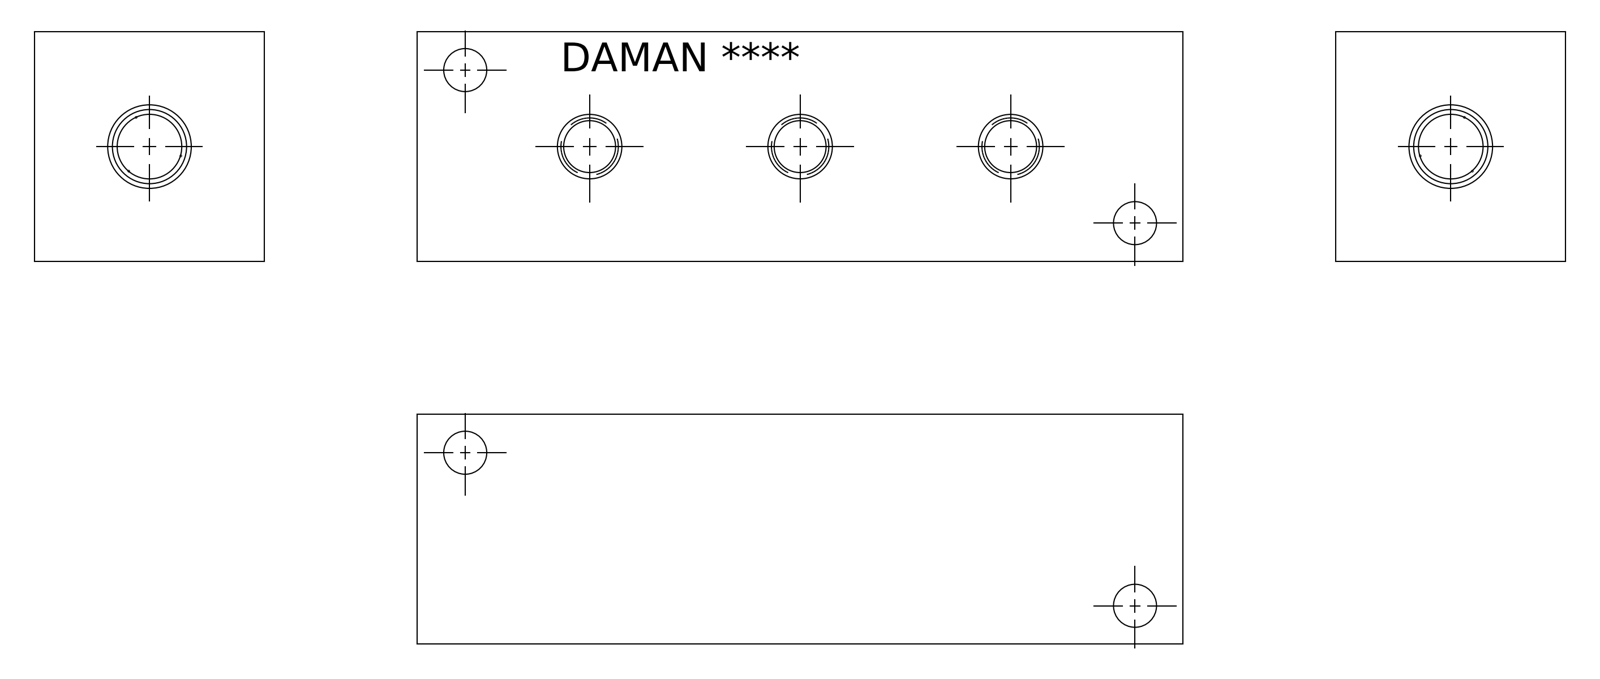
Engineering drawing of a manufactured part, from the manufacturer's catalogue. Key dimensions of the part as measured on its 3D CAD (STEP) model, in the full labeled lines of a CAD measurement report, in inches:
Part name (STEP PRODUCT): Part_+H0000302P_3D
STEP written by: Autodesk Inventor 2019 (AUTOMOTIVE_DESIGN)
Units: inches
Bodies: 1 solid, 343 faces (214 planar, 18 cylindrical, 111 other)
Overall size (bounding box): 5 × 1.5 × 1.5
Volume: 10.54 in³ · Surface area: 42.21 in²
Round holes (diameter × count): ⌀0.281 ×4, ⌀0.332 ×3, ⌀0.407 ×3, ⌀0.422 ×1, ⌀0.546 ×1
Main face-to-face distances: 1.5, 5, 0.449, 4.551, 1.461, 0.039, 1.19, 0.27, 0.31, 4.102
Hole centre spacings: 2.244, 4.489, 0.954, 0.955, 1.375, 1.375, 2.75, 3.598
